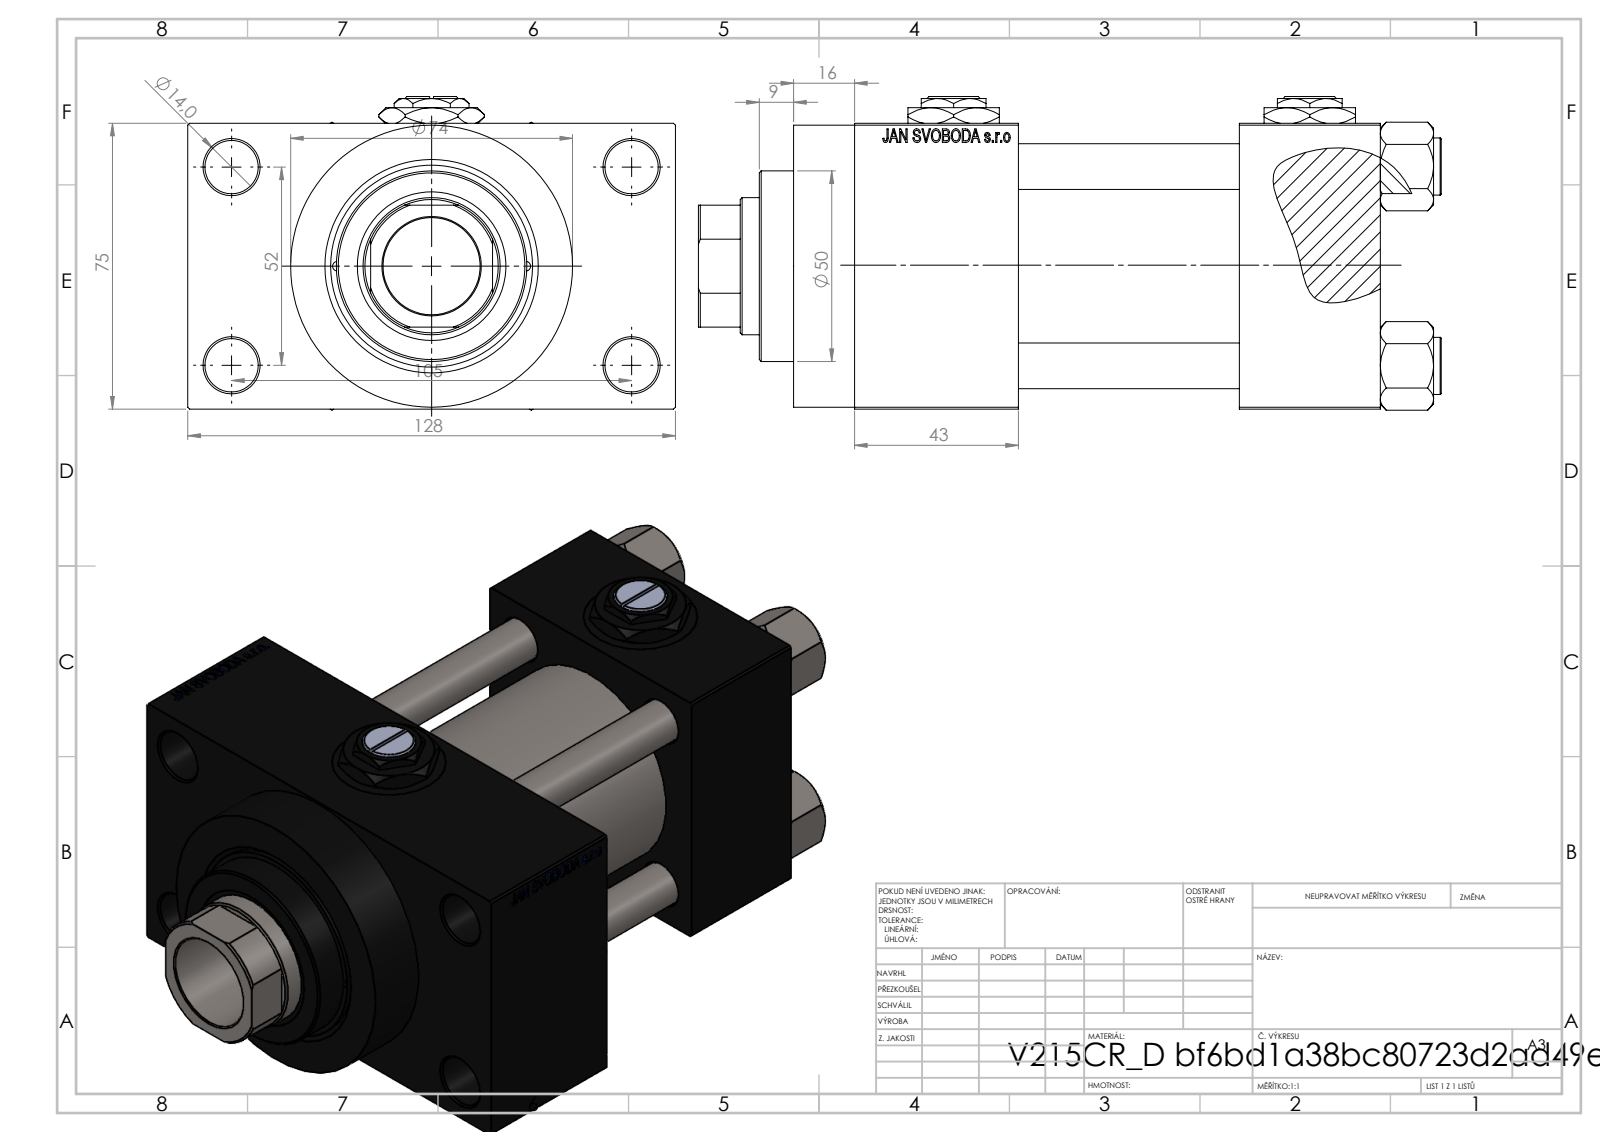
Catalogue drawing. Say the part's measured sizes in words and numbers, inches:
The part is named "NUT_M5_D; V215CR_VCP_D; V215CR_D_Body; V215_VC_A (+2 more)". Its 3-D file was written by "SolidWorks 2019 (CONFIG_CONTROL_DESIGN)". It is 13 solids with 1214 faces: 549 planar, 103 cylindrical and 562 other. Overall it measures 7.677 by 5.039 by 3.239 inches. Its volume is 49.59 cubic inches and its surface area 278.6 square inches. Round holes: 4 of diameter 0.472, 4 of diameter 0.551, 4 of diameter 0.825, 4 of diameter 1.181, 3 of diameter 0.276, 2 of diameter 0.098, 1 of diameter 1.004, 1 of diameter 1.417, 1 of diameter 1.535, 1 of diameter 1.614, 1 of diameter 2.087. Round bosses or shafts: 4 of diameter 0.591, 1 of diameter 2.913, 1 of diameter 2.205, 1 of diameter 1.969. Partial cylindrical surfaces (rounded edges, fillets, slot ends): 1 of radius 0.689. The main face-to-face distances are 2.953, 2.283, 1.457, 3.74, 1.043, 5.433, 1.693, 3.976, 3.996, 0.63. The hole center spacings are 1.031, 1.037, 1.456, 1.497, 2.059, 2.253, 2.3, 2.307.
